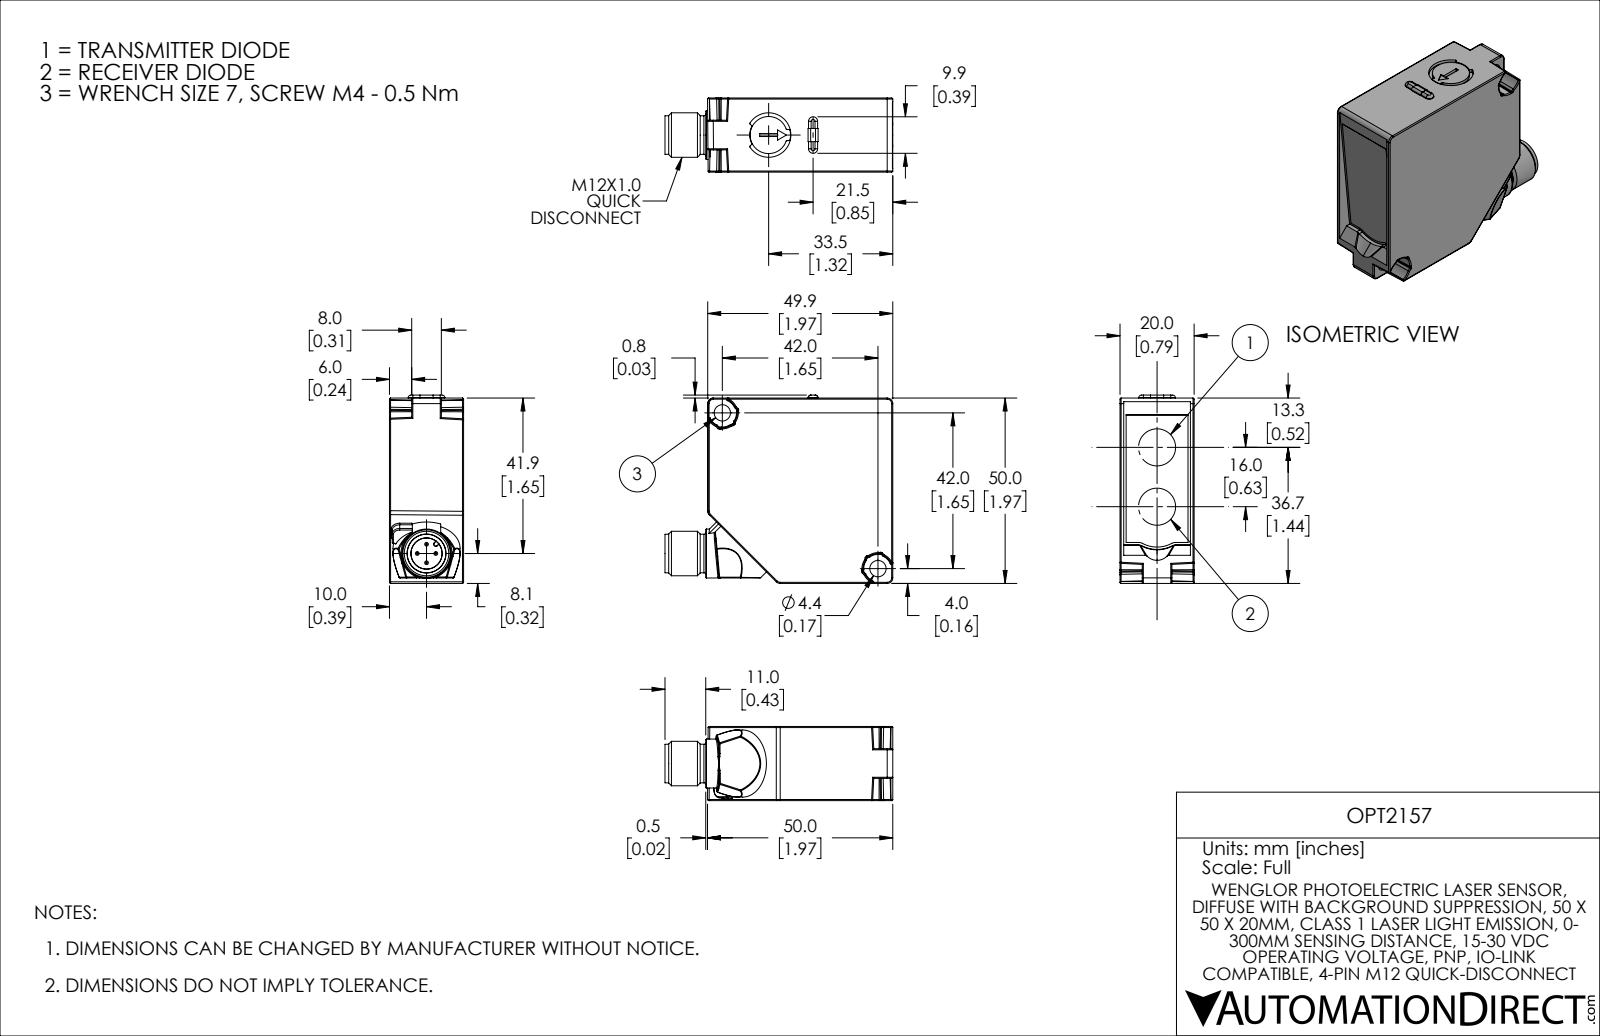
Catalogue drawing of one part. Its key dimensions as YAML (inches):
part_name: "OPT2157_58"
step_written_by: "SolidWorks 2019 (AUTOMOTIVE_DESIGN)"
units: inches
bodies: {solids: 3, faces: 350, planar: 113, cylindrical: 122, other: 115}
overall_size: [2.774, 2, 0.787]
volume: 2.816
surface_area: 15.66
round_holes:
  - {diameter: 0.173, count: 2}
  - {diameter: 0.472, count: 1}
  - {diameter: 0.713, count: 1}
round_bosses_or_shafts:
  - {diameter: 0.039, count: 4}
  - {diameter: 0.008, count: 2}
  - {diameter: 0.52, count: 1}
  - {diameter: 0.472, count: 1}
  - {diameter: 0.409, count: 1}
  - {diameter: 0.394, count: 1}
partial_cylinders:
  - {radius: 0.012, count: 64}
  - {radius: 0.008, count: 8}
  - {radius: 0.059, count: 5}
  - {radius: 0.079, count: 5}
  - {radius: 0.028, count: 4}
  - {radius: 0.048, count: 2}
  - {radius: 0.201, count: 1}
  - {radius: 0.232, count: 1}
face_to_face_distances: [0.787, 1.969, 0.039, 0.748, 0.236, 0.551, 0.197, 0.512, 0.058, 1.911]
hole_center_spacings: [2.339]
